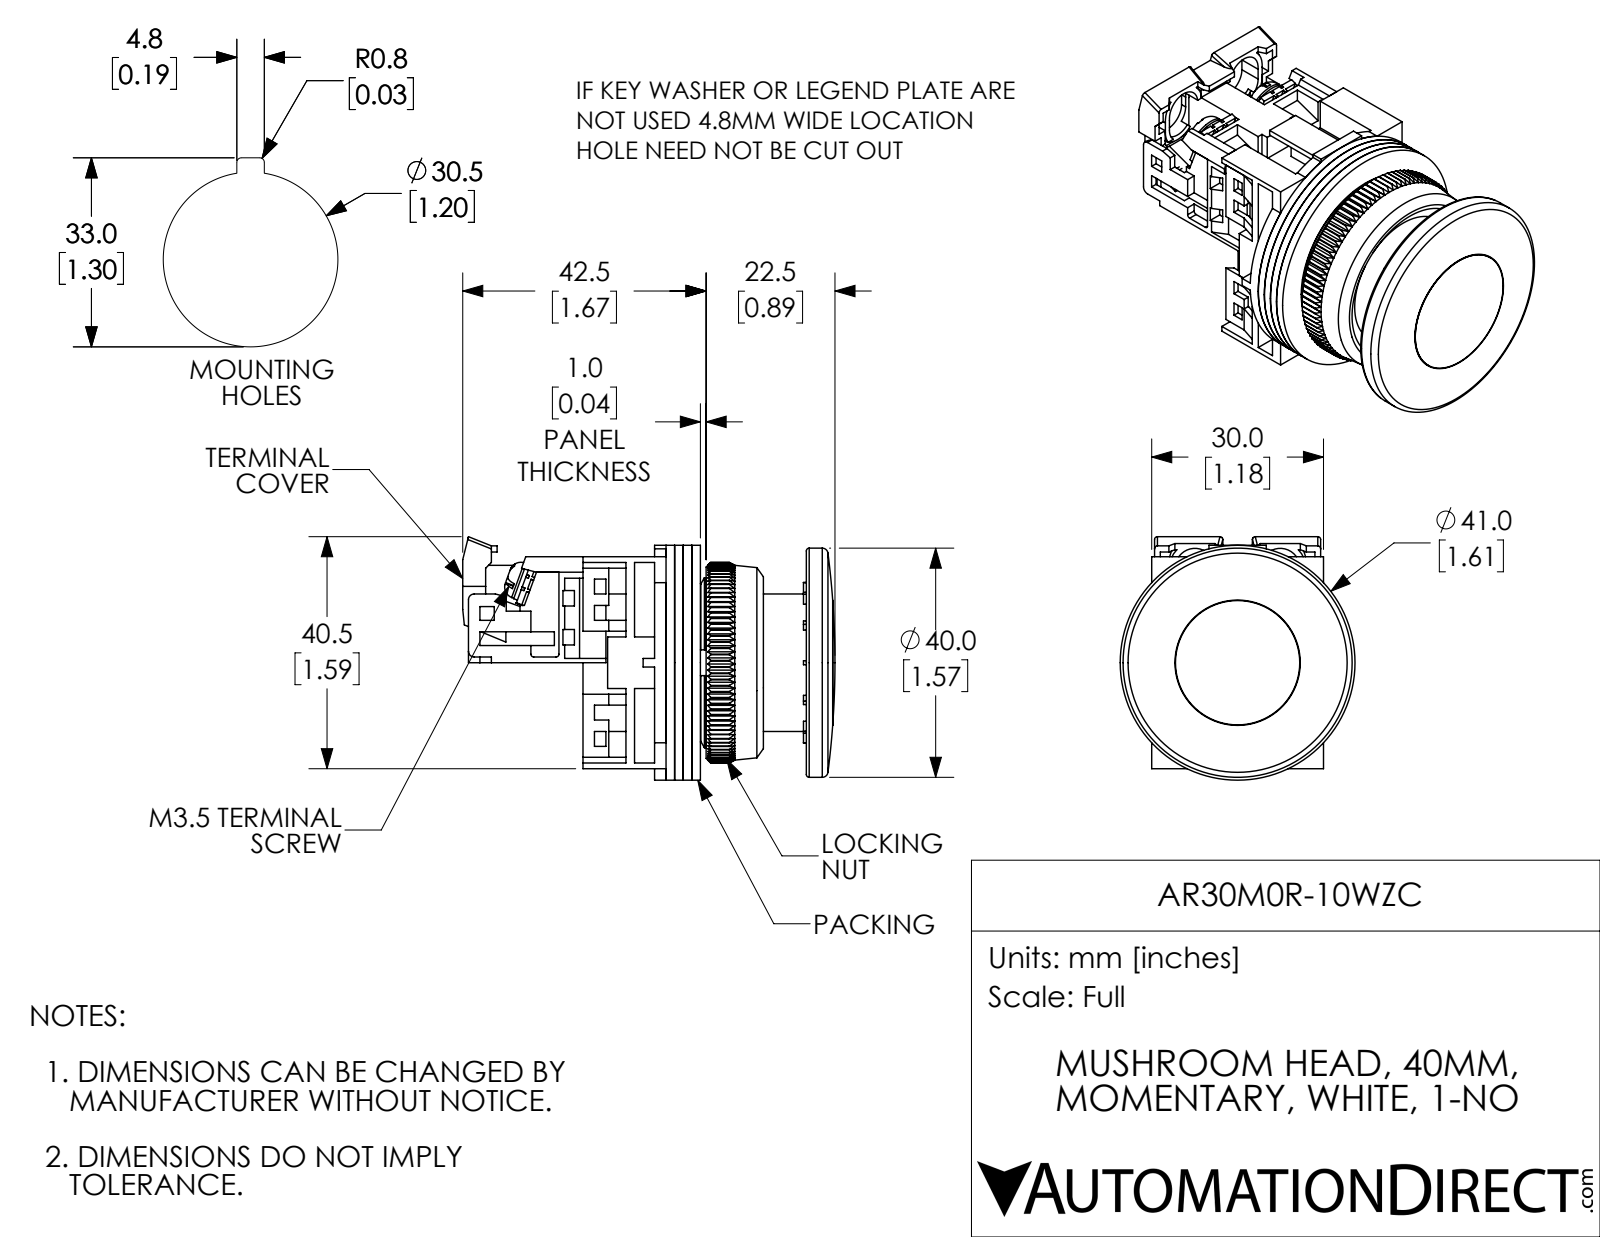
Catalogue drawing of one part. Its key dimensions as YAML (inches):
part_name: "AR30M0R-10WZC"
step_written_by: "SolidWorks 2017 (AUTOMOTIVE_DESIGN)"
units: inches
bodies: {solids: 15, faces: 1278, planar: 819, cylindrical: 260, other: 199}
overall_size: [2.559, 1.673, 1.614]
volume: 2.225
surface_area: 48.33
round_holes:
  - {diameter: 0.138, count: 4}
  - {diameter: 0.142, count: 2}
  - {diameter: 0.118, count: 1}
  - {diameter: 0.709, count: 1}
  - {diameter: 0.945, count: 1}
  - {diameter: 1.122, count: 1}
  - {diameter: 1.252, count: 1}
  - {diameter: 1.417, count: 1}
round_bosses_or_shafts:
  - {diameter: 0.26, count: 2}
  - {diameter: 0.138, count: 2}
  - {diameter: 1.614, count: 1}
  - {diameter: 1.575, count: 1}
  - {diameter: 1.181, count: 1}
  - {diameter: 0.854, count: 1}
partial_cylinders:
  - {radius: 0.059, count: 8}
  - {radius: 0.02, count: 6}
  - {radius: 0.039, count: 2}
  - {radius: 0.138, count: 2}
  - {radius: 0.177, count: 2}
  - {radius: 0.118, count: 1}
  - {radius: 0.398, count: 1}
  - {radius: 0.449, count: 1}
face_to_face_distances: [0.059, 0.118, 0.177, 0.039, 0.079, 0.689, 0.728, 0.866, 0.807, 1.417]
hole_center_spacings: [0.579, 0.61]
